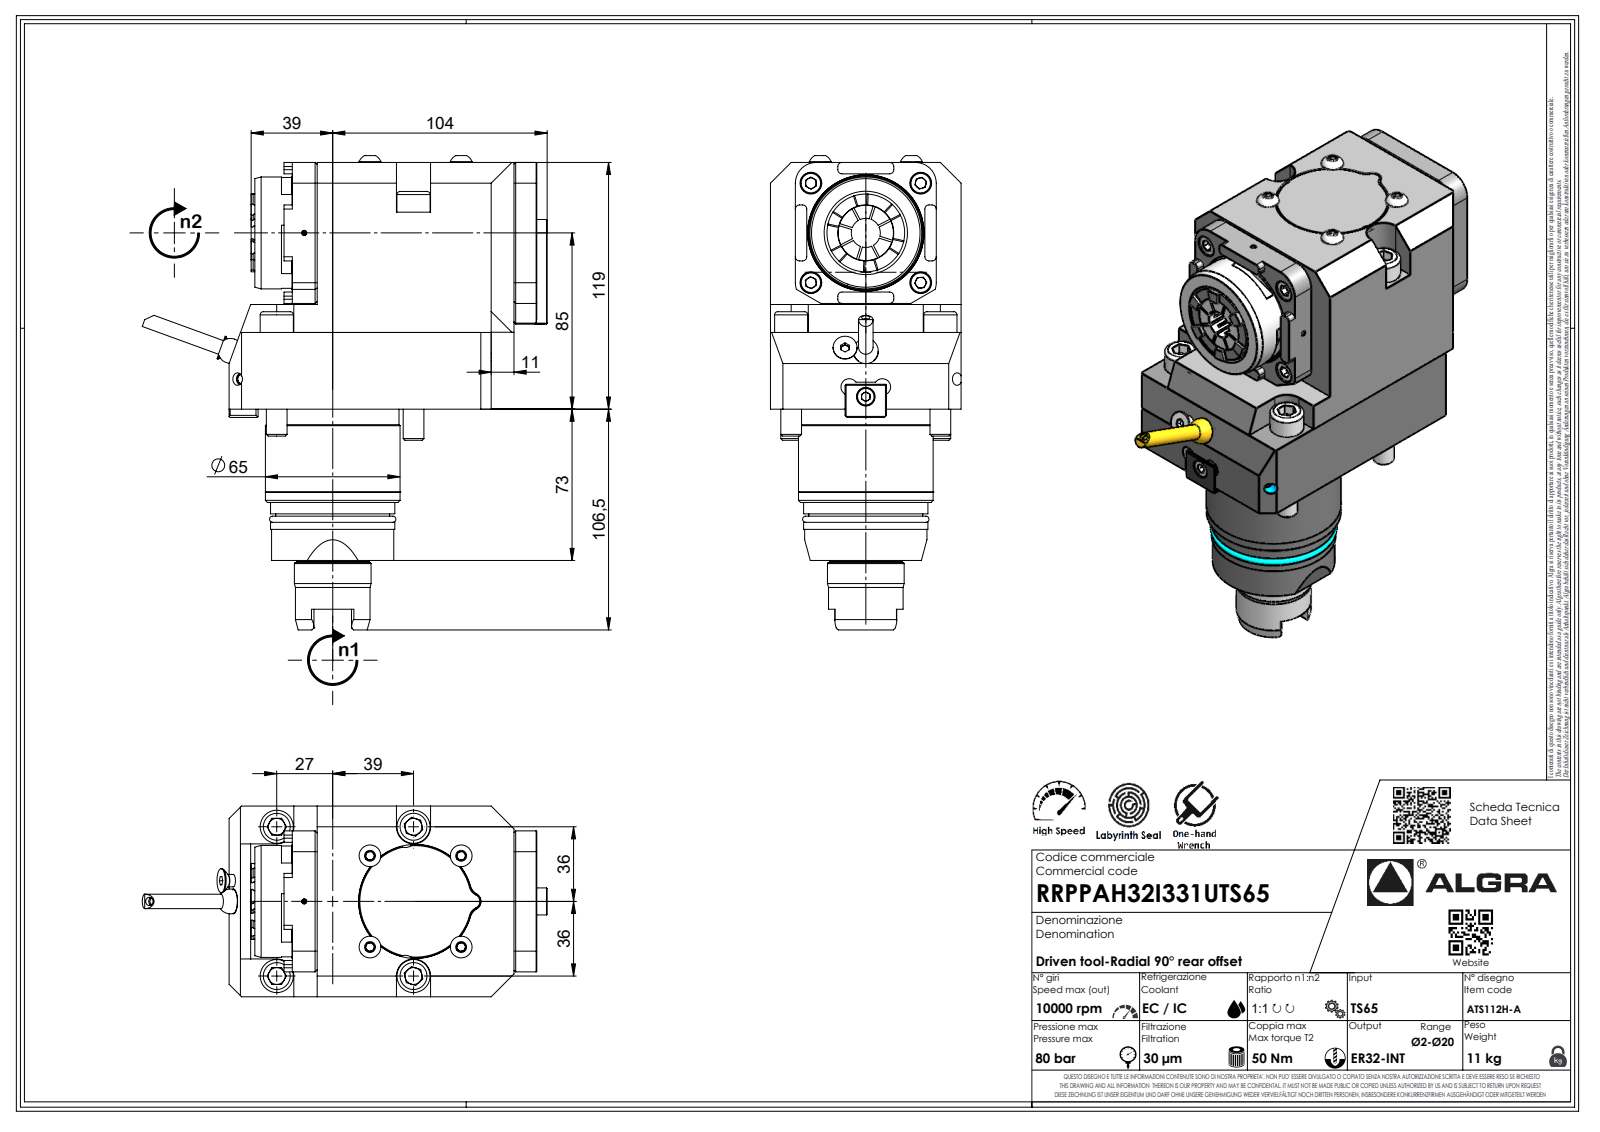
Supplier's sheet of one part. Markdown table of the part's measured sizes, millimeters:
| quantity | value |
| --- | --- |
| part name | RRPPAH32I331UTS65 |
| STEP written by | SolidWorks 2023 (AUTOMOTIVE_DESIGN) |
| units | millimeters |
| bodies | 1 solid, 592 faces (349 planar, 90 cylindrical, 153 other) |
| overall size | 228.8 × 195.41 × 92 |
| volume | 1 570 000 mm³ |
| surface area | 103 850 mm² |
| round holes (diameter × count) | 2.1 × 1, 4 × 1 |
| round bosses / shafts (diameter × count) | 10.5 × 4, 10 × 4, 16 × 2, 65 × 1, 64.98 × 1, 64 × 1, 60 × 1, 59 × 1 |
| partial cylindrical surfaces (radius × count) | 2 × 16, 0.33 × 7, 0.52 × 7, 3.7 × 7, 10 × 6, 0.75 × 4, 8.25 × 2, 0.21 × 1 |
| main face-to-face distances | 92, 119, 12, 22, 50.5, 11, 114.05, 136.05, 68.5, 80 |
